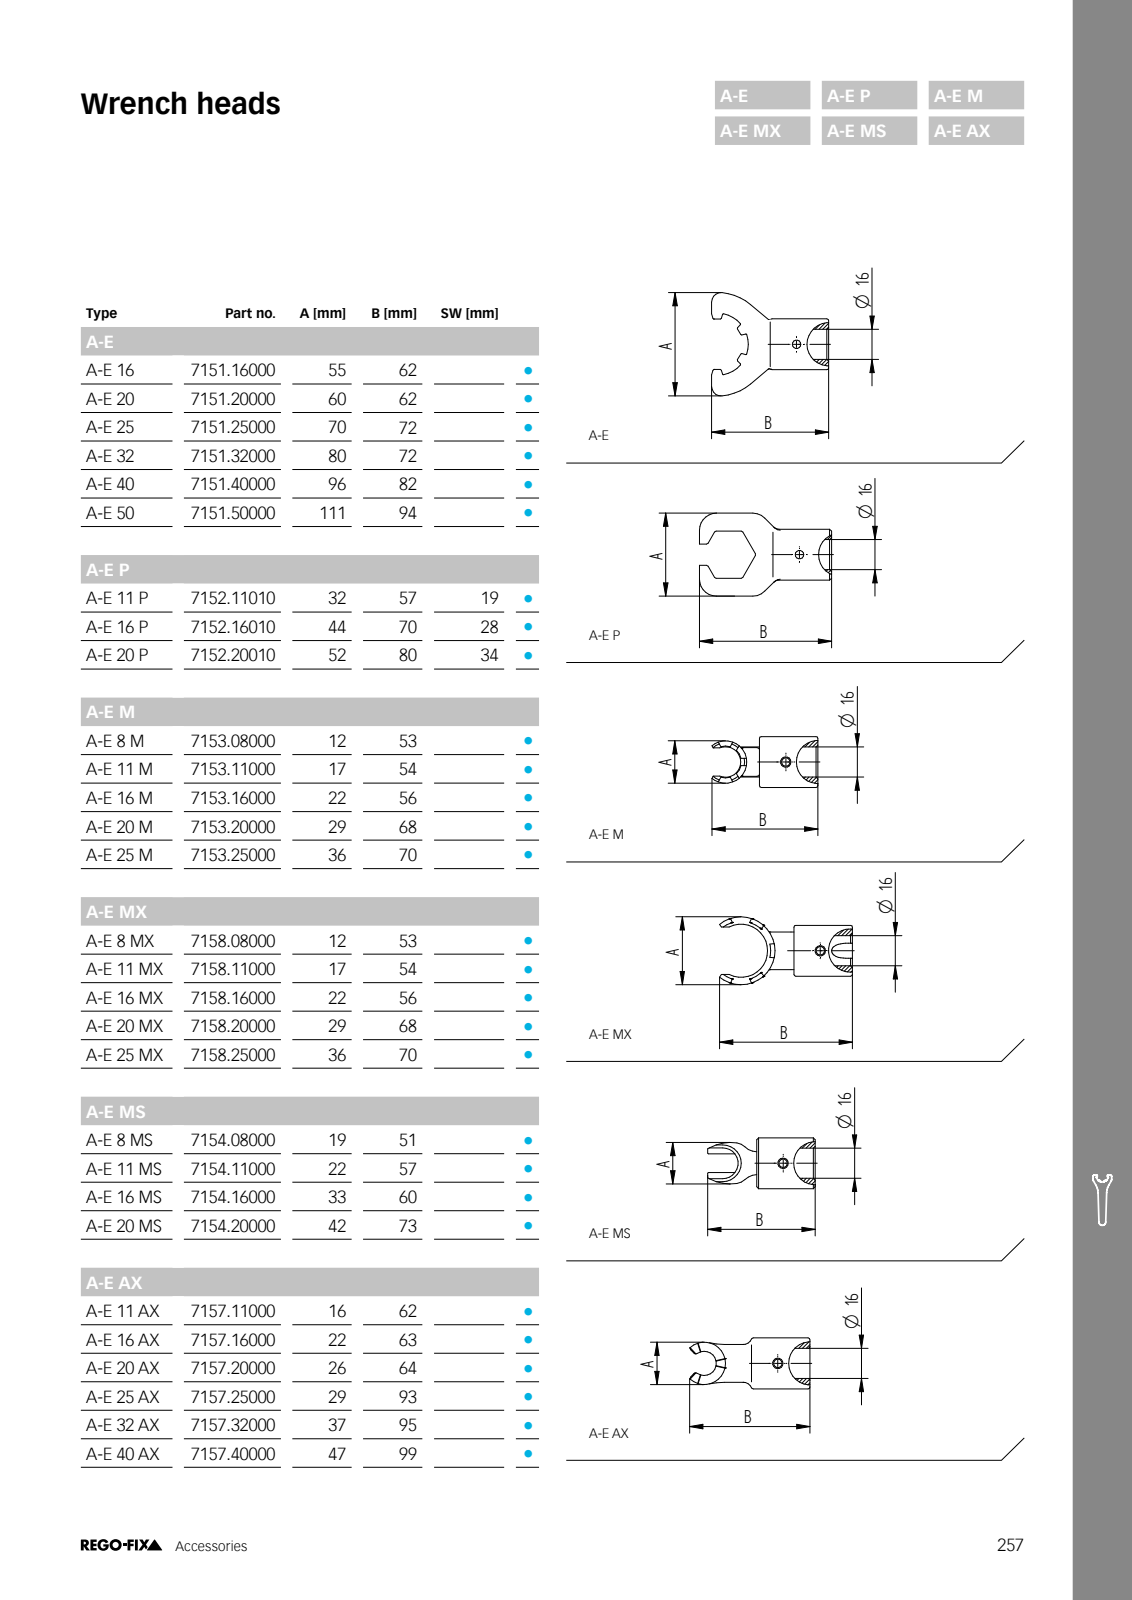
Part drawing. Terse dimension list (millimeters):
name: 6401-1 TORCO-FIX II Adjustable Torque Wrench 40-200 Nm (16mm interface); 6401-2 TORCO-FIX II Adjustable Torque Wrench 40-200 Nm (16mm interface); 6401 TORCO-FIX II Adjustable Torque Wrench 40-200 Nm (16mm interface)
written by: Alibre (AP242_MANAGED_MODEL_BASED_3D_ENGINEERING_MIM_LF)
unit: mm
bodies: 2 solids, 84 faces (18 planar, 30 cylindrical, 36 other)
size: 467.52 × 44.3 × 44.3
volume: 289 265 mm³; area: 49 377 mm²
bosses: 1× ⌀44.3, 1× ⌀36, 1× ⌀33, 1× ⌀32, 1× ⌀25, 1× ⌀24, 1× ⌀22.6, 1× ⌀19
rounds: 5× R2, 1× R20
face distances: 20, 2, 18, 338.5, 31.5, 307, 33.5, 305, 459.5, 428
